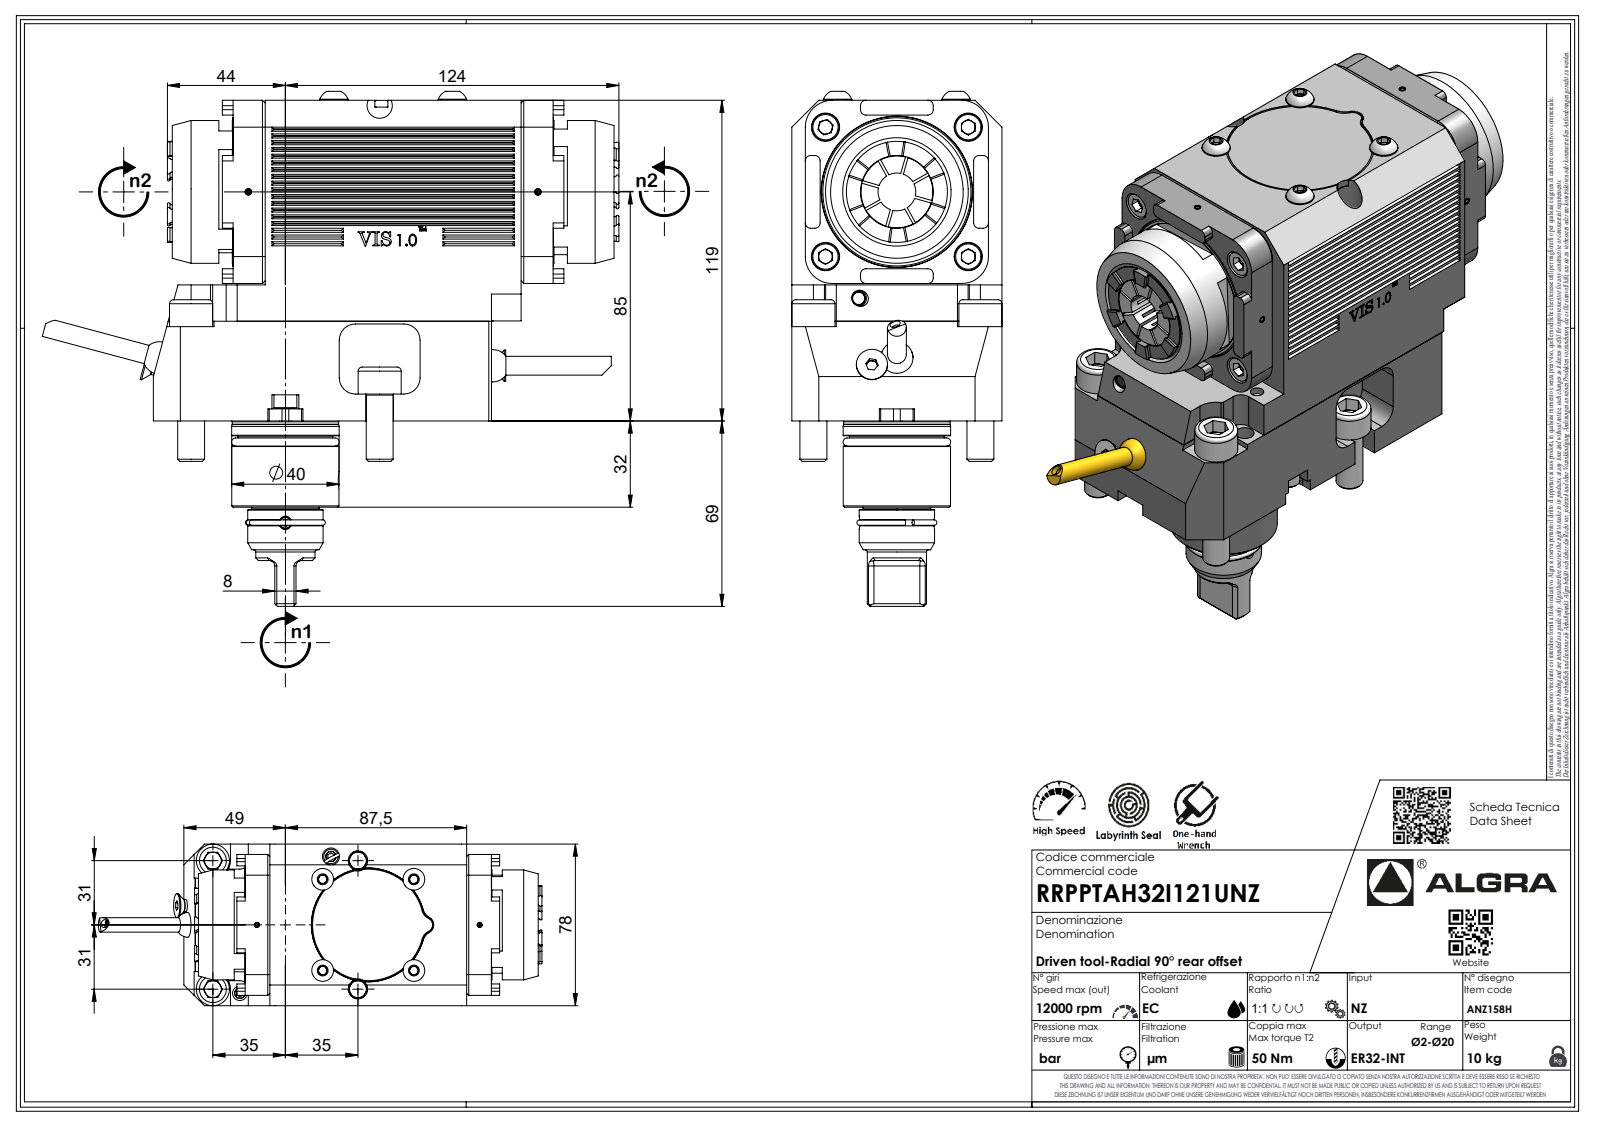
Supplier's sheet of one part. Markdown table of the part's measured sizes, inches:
| quantity | value |
| --- | --- |
| part name | RRPPTAH32I121UNZ |
| STEP written by | SolidWorks 2023 (AUTOMOTIVE_DESIGN) |
| units | inches |
| bodies | 1 solid, 579 faces (367 planar, 110 cylindrical, 102 other) |
| overall size | 8.356 × 7.524 × 3.071 |
| volume | 76.34 in³ |
| surface area | 141.2 in² |
| round holes (diameter × count) | 0.157 × 2, 0.083 × 1 |
| round bosses / shafts (diameter × count) | 0.413 × 4, 0.394 × 4, 0.63 × 2, 0.276 × 2, 2.087 × 1, 1.571 × 1, 1.567 × 1, 1.555 × 1 |
| partial cylindrical surfaces (radius × count) | 0.079 × 24, 0.013 × 7, 0.02 × 7, 0.146 × 7, 0.394 × 4, 0.039 × 2, 0.161 × 2, 0.335 × 2 |
| main face-to-face distances | 3.071, 4.685, 0.197, 0.89, 5.567, 2.874, 2.677, 1.358, 5.098, 0.469 |
